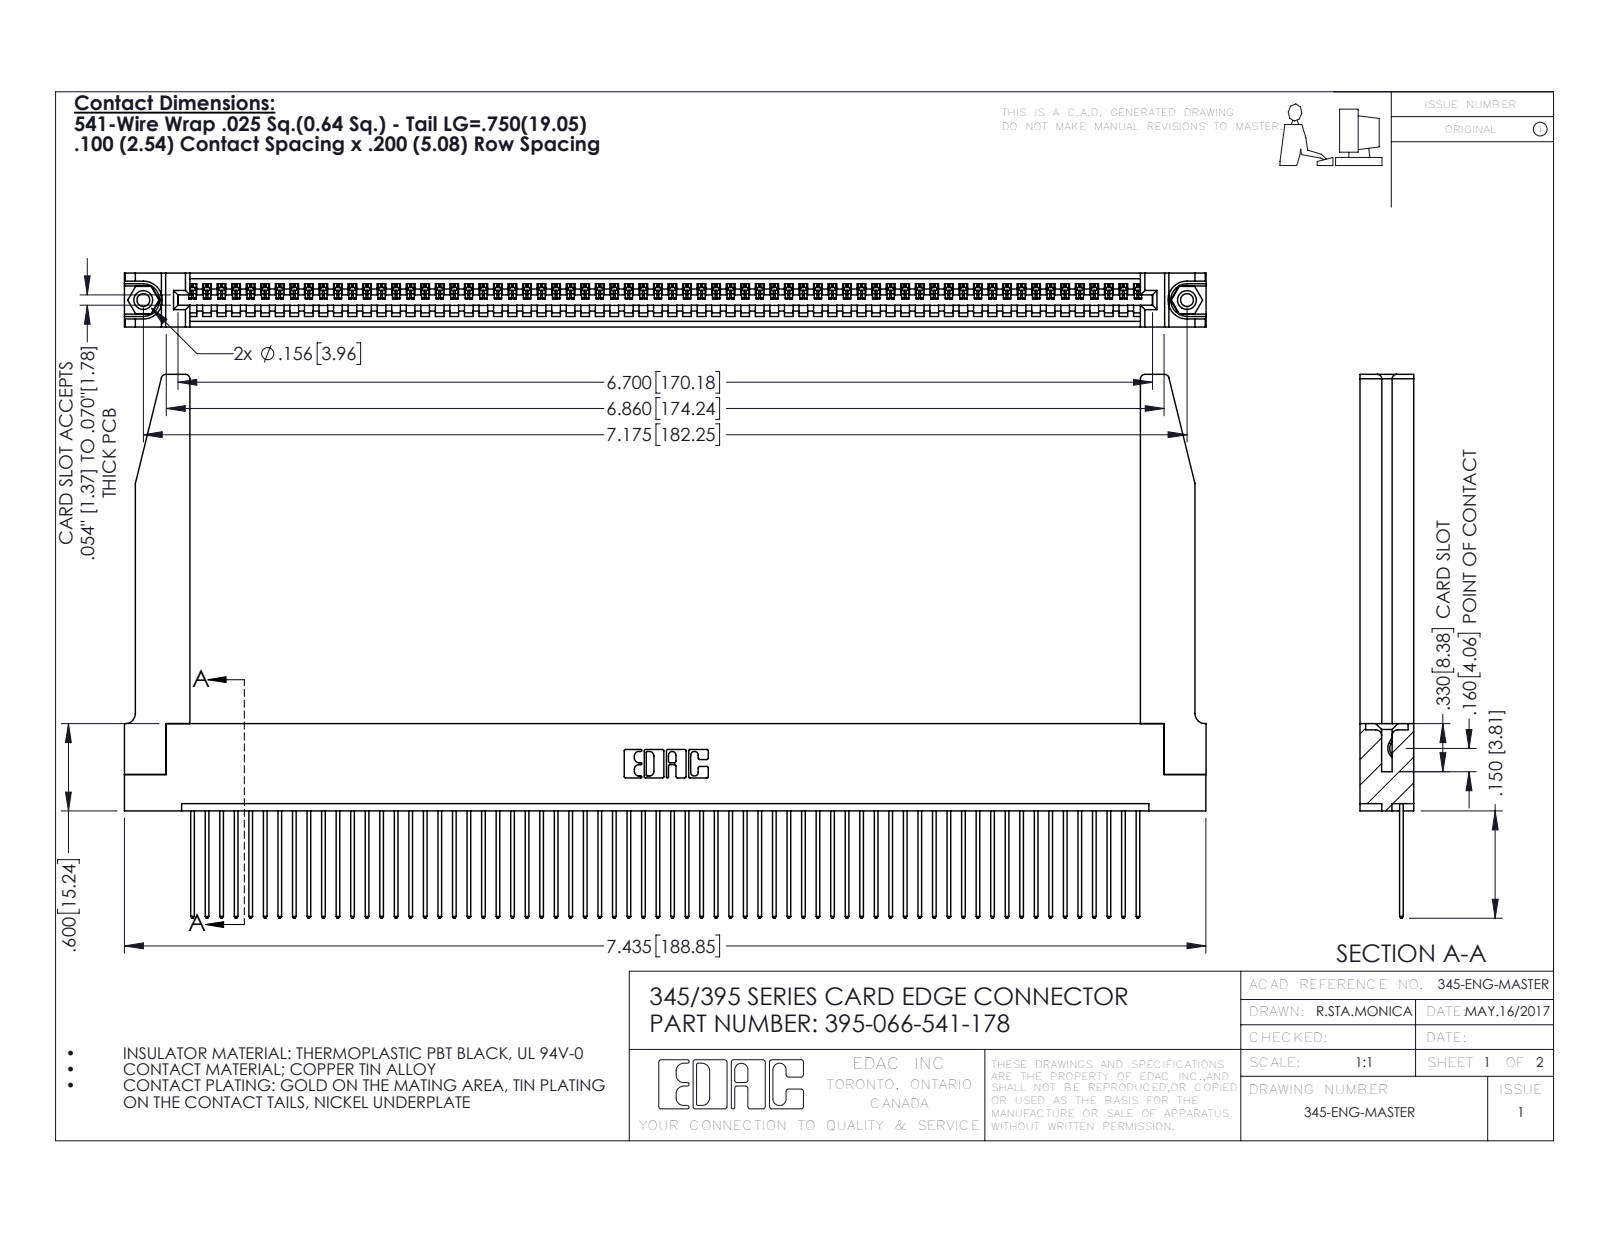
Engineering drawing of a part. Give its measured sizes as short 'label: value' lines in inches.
name: 395-066-541-178; 345-220-078_345-220-078; 345 Part_Flush Mounting Lugs - 0.156 Dia-TH; 345-292-001_345-293-141 (+1 more)
written by: SolidWorks 2016 (CONFIG_CONTROL_DESIGN)
unit: in
bodies: 71 solids, 4188 faces (2862 planar, 1274 cylindrical, 52 other)
size: 7.436 × 3.737 × 0.37
volume: 1.594 in³; area: 50.91 in²
holes: 2× ⌀0.089, 2× ⌀0.125, 2× ⌀0.156, 1× ⌀0.064
bosses: 2× ⌀0.155
rounds: 132× R0.006, 132× R0.01, 22× R0.01, 8× R0.03, 6× R0.007, 6× R0.031, 3× R0.026, 2× R0.031
face distances: 0.072, 0.298, 0.37, 0.098, 0.272, 0.025, 0.2, 0.225, 0.149, 0.15
hole spacings: 0.27, 6.939, 7.175
